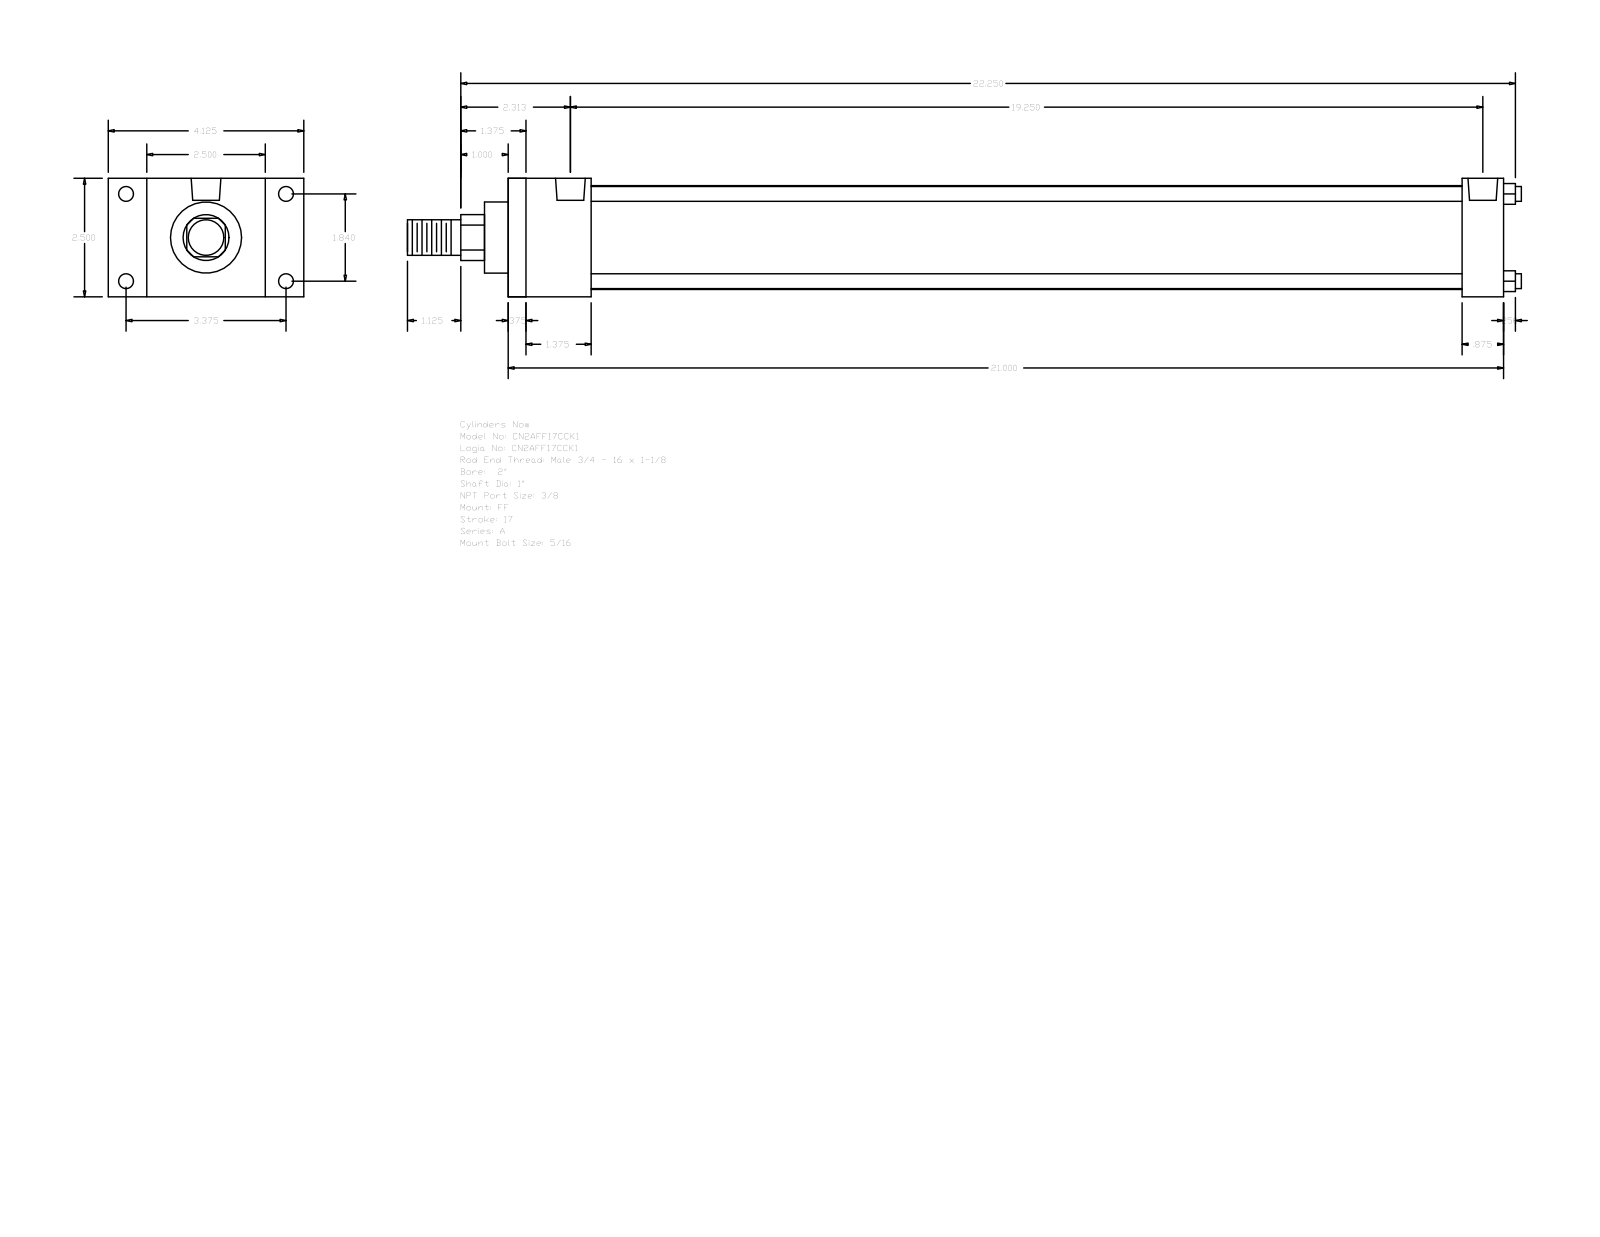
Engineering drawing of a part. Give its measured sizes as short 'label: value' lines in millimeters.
name: A_FF__0200_1
written by: GSSL Pune (CONFIG_CONTROL_DESIGN)
unit: mm
bodies: 0 solids, 92 faces (64 planar, 28 cylindrical, 0 other)
size: 596.9 × 104.78 × 63.5
holes: 4× ⌀5.56, 4× ⌀7.94, 2× ⌀15.93
bosses: 4× ⌀7.94, 1× ⌀55.63, 1× ⌀38.1, 1× ⌀25.4, 1× ⌀19.05
rounds: 1× R12.29
face distances: 63.5, 533.4, 523.88, 9.52, 22.22, 20.64, 44.45, 511.18, 34.93, 501.66
hole spacings: 46.74, 85.72, 97.63, 483.38, 1.59, 3.98, 484.97, 487.36
